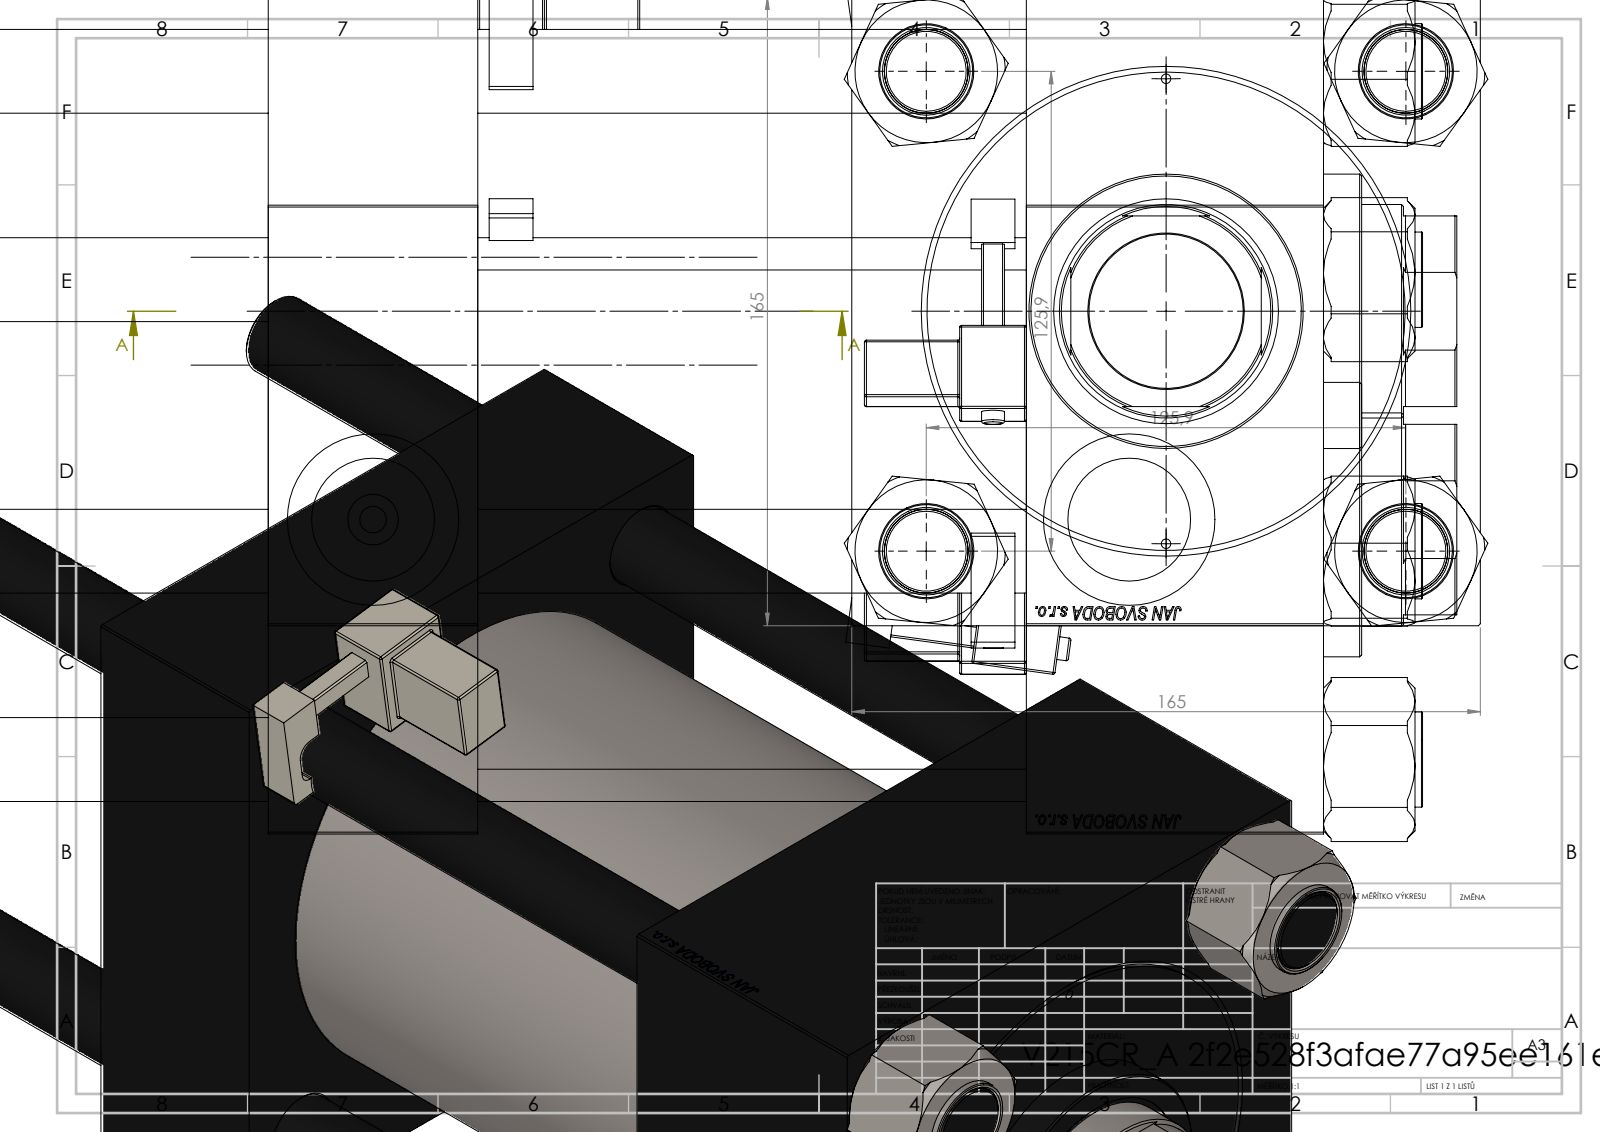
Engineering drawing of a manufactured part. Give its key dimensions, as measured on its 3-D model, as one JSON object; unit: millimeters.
{"part_name": "NUT_M5; V215_VC_A; V215CR_BODY_A; V215CR_VCP (+2 more)", "step_written_by": "SolidWorks 2019 (CONFIG_CONTROL_DESIGN)", "units": "millimeters", "bodies": {"solids": 13, "faces": 1342, "planar": 628, "cylindrical": 142, "other": 572}, "overall_size": [393, 190.66, 168.94], "volume_mm3": 5034000, "surface_area_mm2": 636851, "round_holes": [[22, 4], [2.5, 2], [7, 2], [32.24, 2], [45, 2], [40.5, 1], [56, 1], [59, 1], [96, 1], [125, 1], [125.5, 1]], "round_bosses_or_shafts": [[25, 4], [6, 2], [131, 1], [72, 1]], "partial_cylinders_radius": [[0.5, 48], [1, 2], [2.5, 2], [4, 2], [27, 1]], "face_to_face_distances": [165, 55, 277, 222, 199, 144, 78, 248.3, 193.3, 49.3], "hole_center_spacings": [62.98, 89.02, 125.9, 139.02, 61, 178.05, 122, 198.5]}
